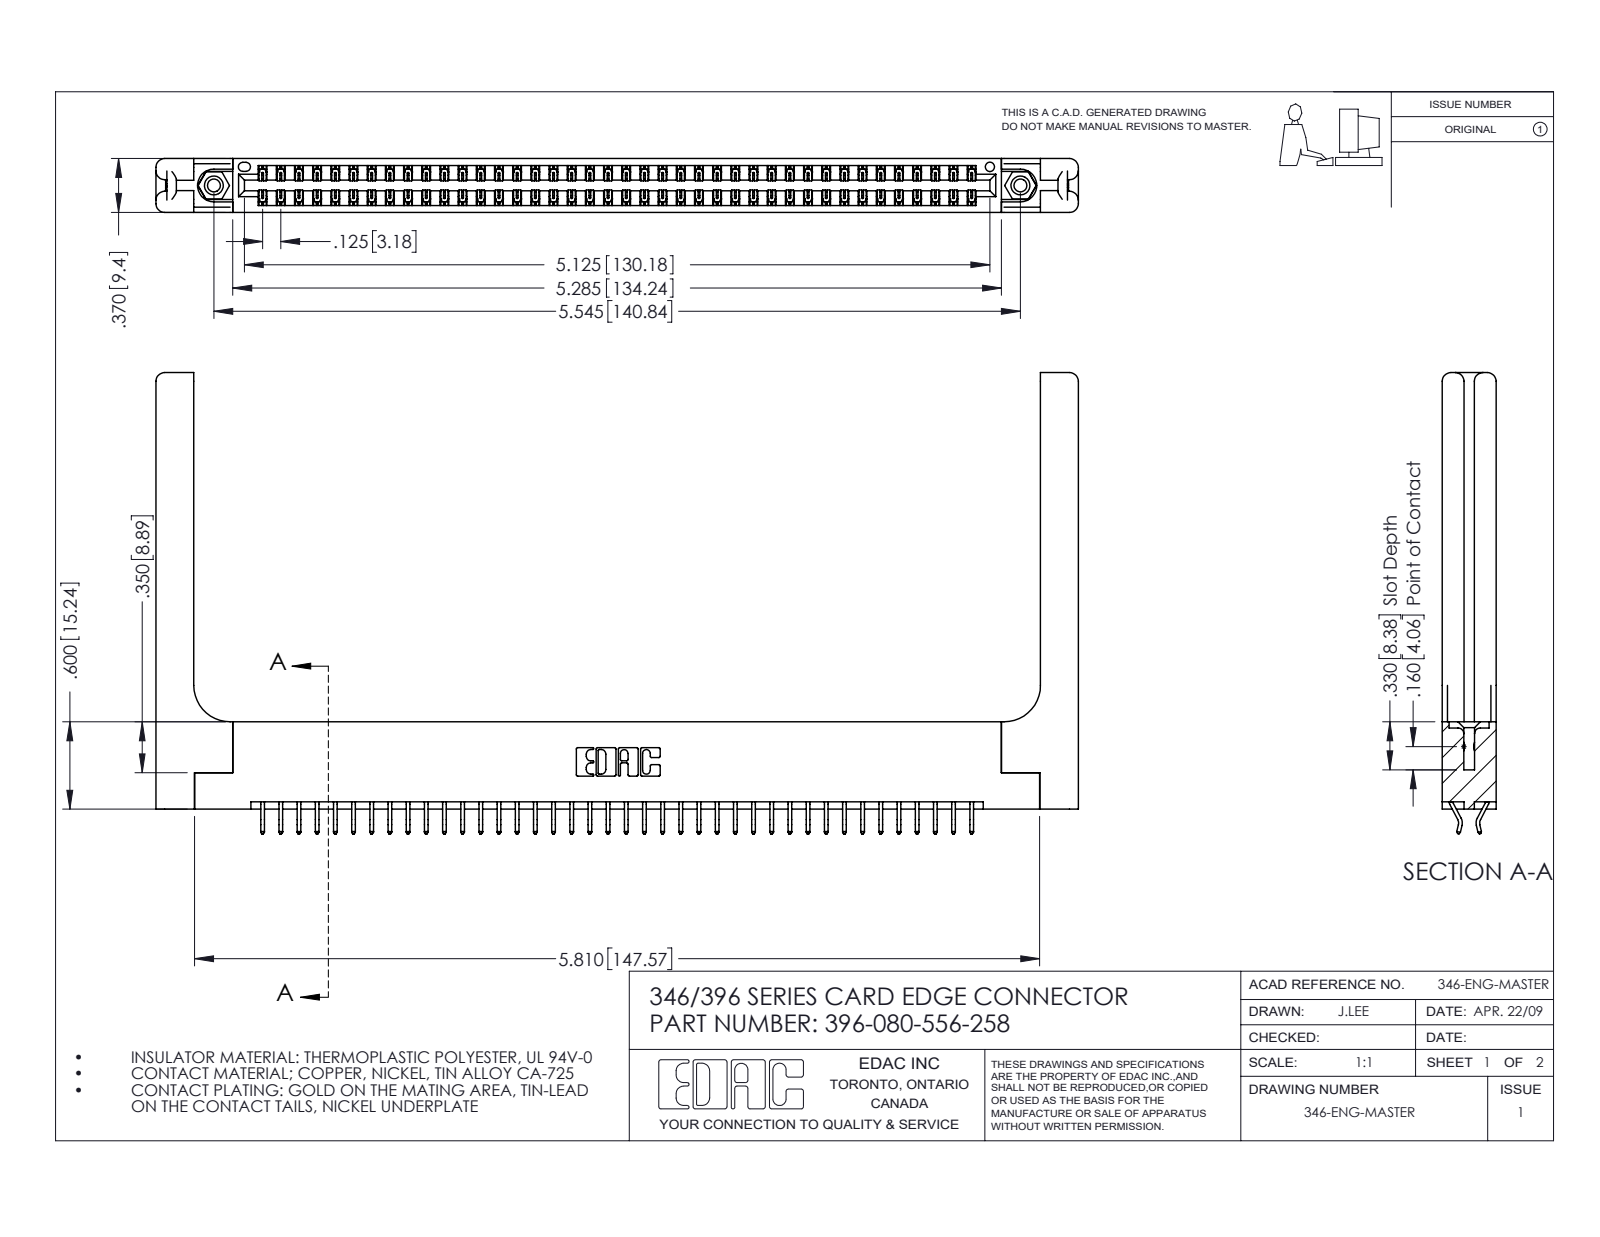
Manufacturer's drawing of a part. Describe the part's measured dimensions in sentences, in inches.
The part is named "346 Part_Flush Mounting Lugs - 0.156 Dia-TH; 396-080-556-258; 345-250-001_345-250-001-102; 345-292-001_556 Tail (+1 more)". Its 3-D file was written by "SolidWorks 2016 (CONFIG_CONTROL_DESIGN)". It is 85 solids with 5018 faces: 3344 planar, 1614 cylindrical and 60 other. Overall it measures 6.341 by 3.17 by 0.37 inches. Its volume is 1.415 cubic inches and its surface area 40.97 square inches. Round holes: 2 of diameter 0.089, 2 of diameter 0.125, 2 of diameter 0.156, 1 of diameter 0.064. Round bosses or shafts: 2 of diameter 0.155. Partial cylindrical surfaces (rounded edges, fillets, slot ends): 120 of radius 0.006, 22 of radius 0.01, 16 of radius 0.06, 6 of radius 0.007, 6 of radius 0.031, 3 of radius 0.026, 2 of radius 0.01, 2 of radius 0.014. The main face-to-face distances are 0.37, 0.048, 0.322, 0.072, 0.15, 0.148, 0.25, 0.025, 0.298, 0.275. The hole center spacings are 0.246, 5.336, 5.545.
